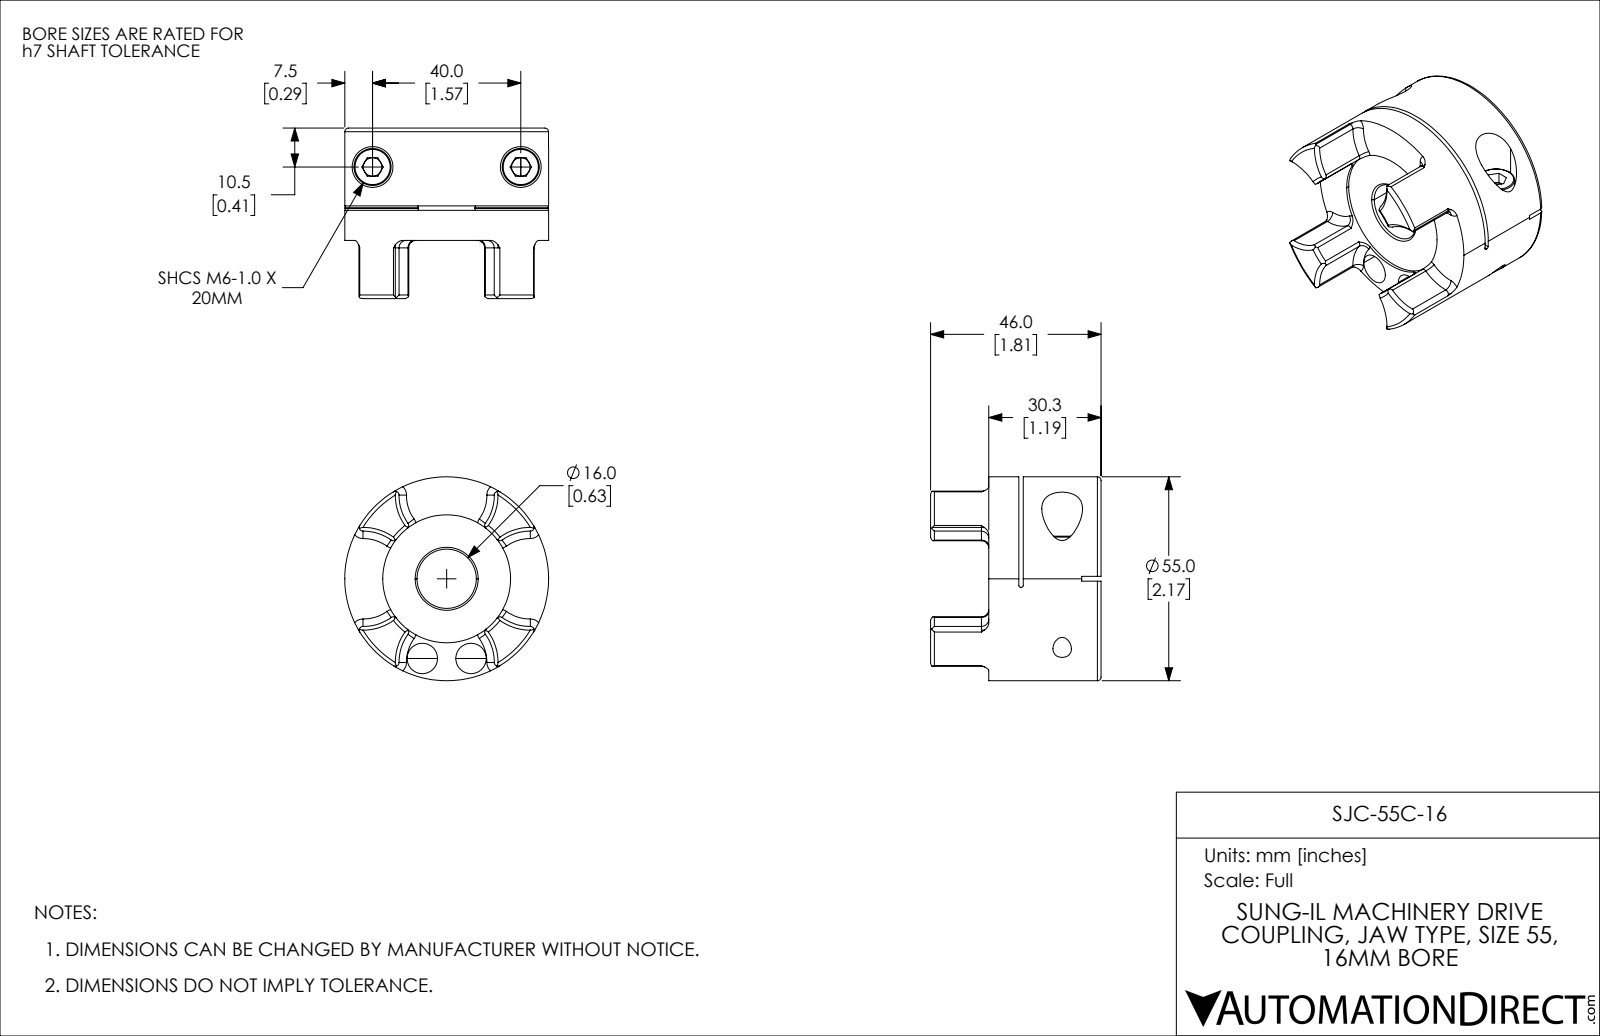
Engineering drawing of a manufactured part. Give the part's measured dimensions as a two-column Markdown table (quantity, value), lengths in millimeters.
| quantity | value |
| --- | --- |
| part name | SJC-55C-16 |
| STEP written by | SolidWorks 2021 (CONFIG_CONTROL_DESIGN) |
| units | millimeters |
| bodies | 3 solids, 206 faces (52 planar, 72 cylindrical, 82 other) |
| overall size | 55 × 55 × 46 |
| volume | 66 409 mm³ |
| surface area | 20 351 mm² |
| round holes (diameter × count) | 5 × 2, 6.4 × 2, 8.2 × 2, 11 × 2, 16 × 1, 34.5 × 1 |
| round bosses / shafts (diameter × count) | 10 × 2, 6 × 2, 55 × 1 |
| partial cylindrical surfaces (radius × count) | 1 × 16, 12.85 × 4, 0.5 × 2, 50 × 1 |
| main face-to-face distances | 22.2, 1.2, 21, 8.1, 9.3, 30.3, 0.8, 7.3, 8.5, 29.5 |
| hole center spacings | 22.47, 13.14, 40 |
